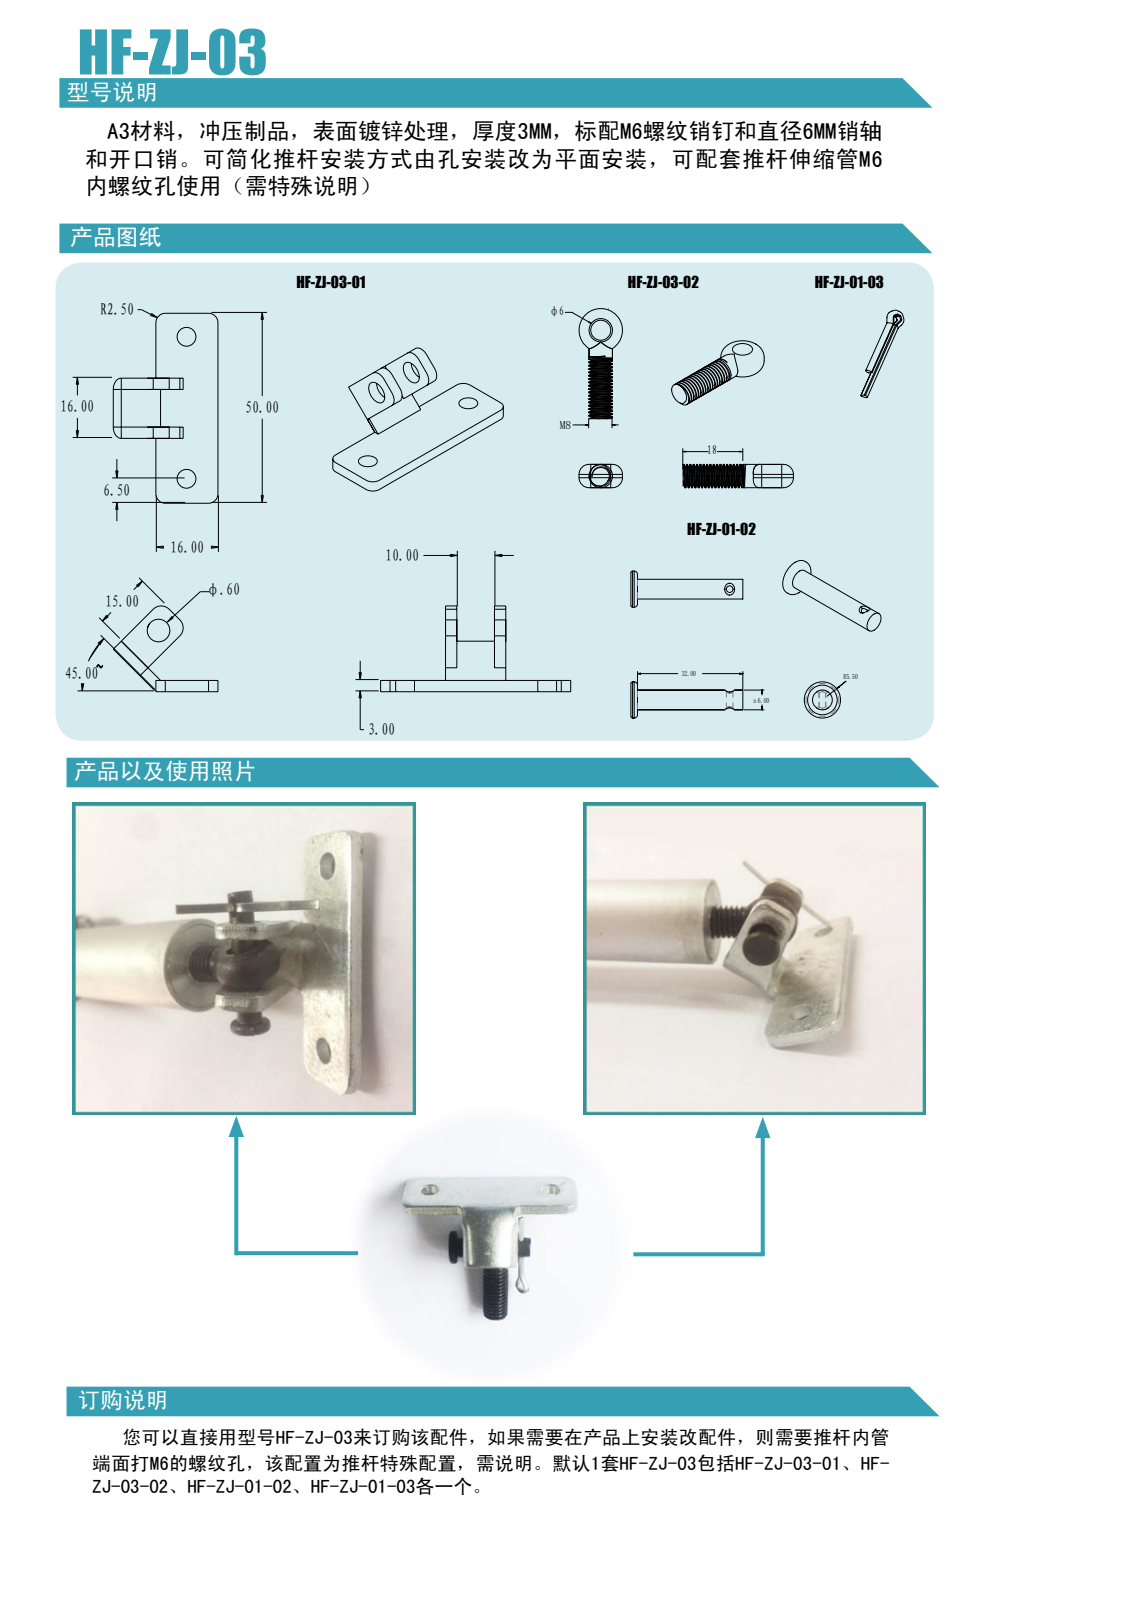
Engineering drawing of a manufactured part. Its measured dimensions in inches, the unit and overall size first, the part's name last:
Units: inches
Overall size (bounding box): 50.486 × 42.763 × 27.799
Round holes (diameter × count): ⌀5 ×2, ⌀6 ×1
Round bosses / shafts (diameter × count): ⌀13 ×1, ⌀7 ×1
Partial cylindrical surfaces — rounded edges, fillets, slot ends (radius × count): R3 ×5, R2.5 ×4
Main face-to-face distances: 3, 13, 3, 16, 10, 9.998, 16.485, 17.243, 20.243, 30.243
Hole centre spacings: 37.737
Volume: 4 989 in³ · Surface area: 4 727 in²
Bodies: 2 solids, 111 faces (35 planar, 60 cylindrical, 16 other)
Part name (STEP PRODUCT): ZJ-03; M4LS; ASM0001_ASM
STEP written by: PRO/ENGINEER BY PARAMETRIC TECHNOLOGY CORPORATION, 2008380 (CONFIG_CONTROL_DESIGN)
